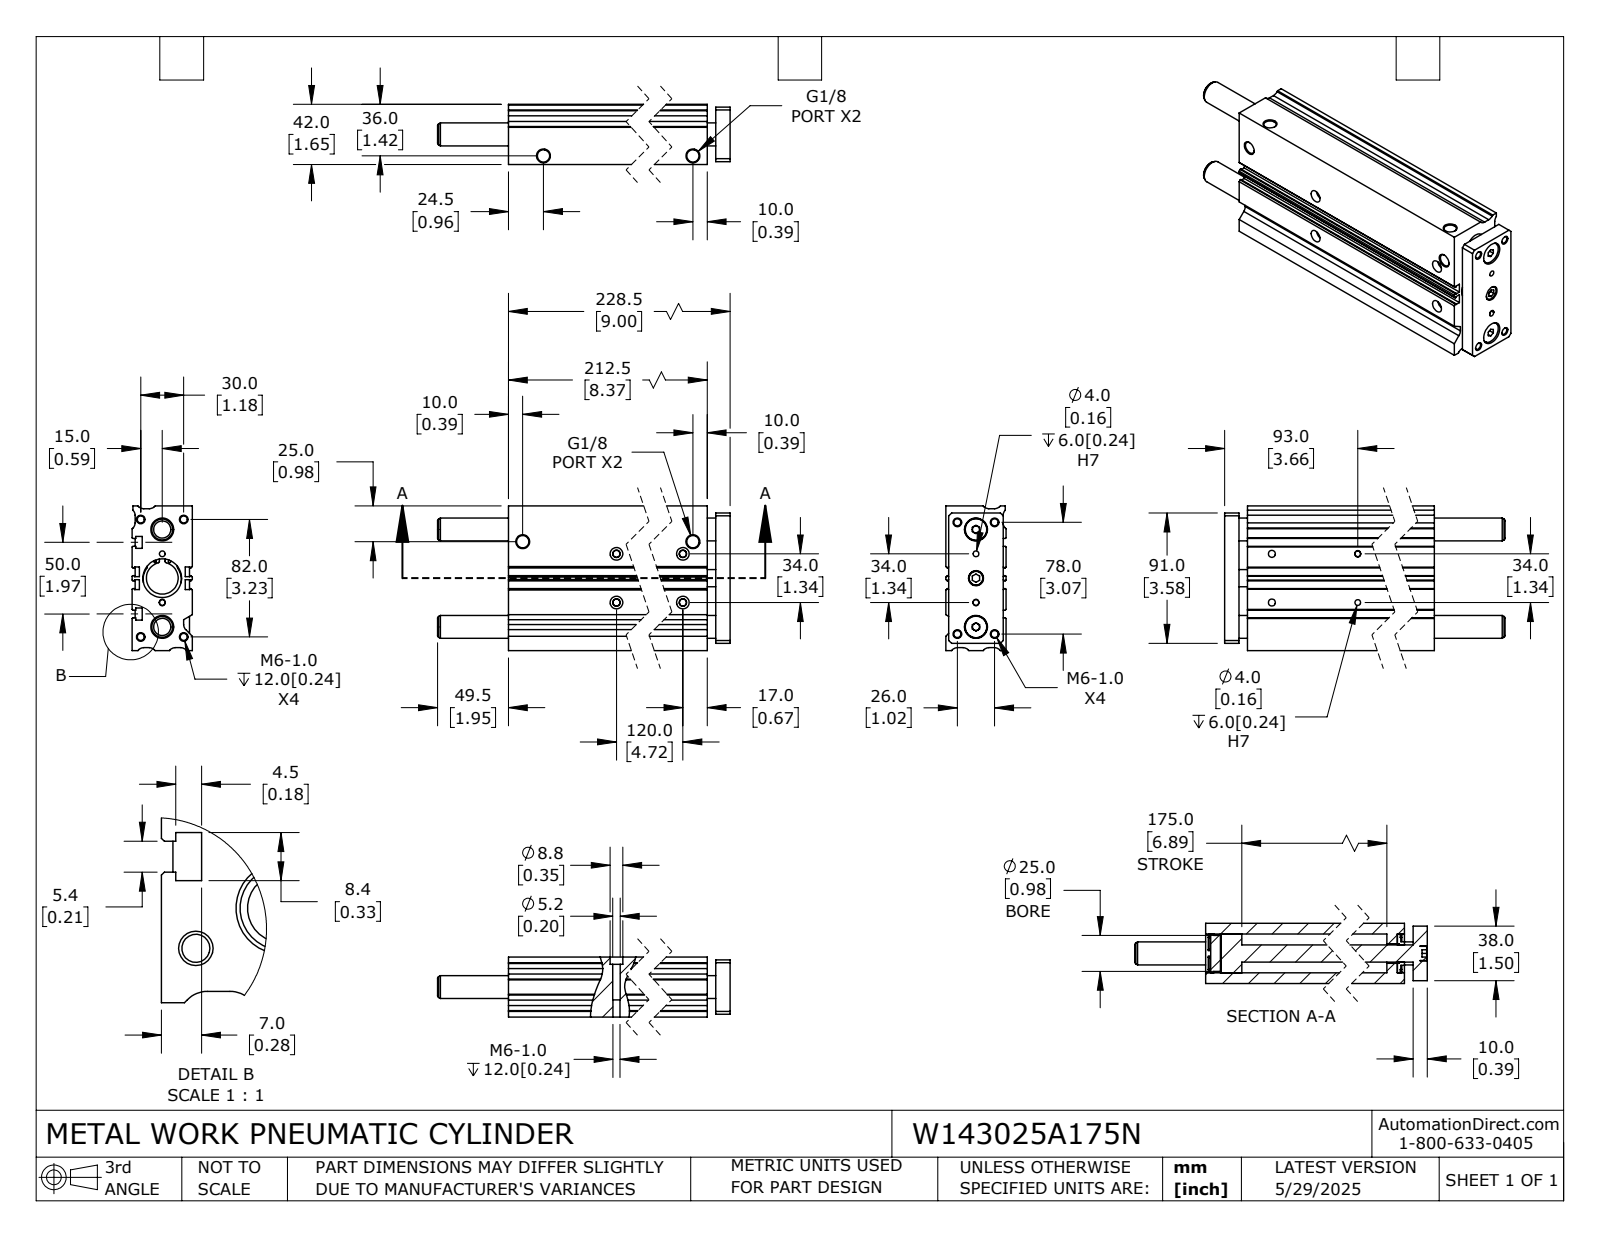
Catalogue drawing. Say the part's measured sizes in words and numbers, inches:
The part is named "W143025A175N_ROD; W143025A175N; W143025A175N_BODY". Its 3-D file was written by "SolidWorks 2024 (CONFIG_CONTROL_DESIGN)". It is 6 solids with 390 faces: 191 planar, 157 cylindrical and 42 other. Overall it measures 10.945 by 3.976 by 1.654 inches. Its volume is 48.04 cubic inches and its surface area 284.7 square inches. Round holes: 8 of diameter 0.194, 4 of diameter 0.067, 4 of diameter 0.157, 4 of diameter 0.194, 4 of diameter 0.205, 4 of diameter 0.337, 4 of diameter 0.346, 2 of diameter 0.63, 1 of diameter 0.413, 1 of diameter 0.472, 1 of diameter 0.539, 1 of diameter 0.874. Round bosses or shafts: 2 of diameter 0.61, 1 of diameter 1.063, 1 of diameter 0.984, 1 of diameter 0.65, 1 of diameter 0.394. Partial cylindrical surfaces (rounded edges, fillets, slot ends): 12 of radius 0.039, 9 of radius 0.197, 8 of radius 0.079, 2 of radius 0.524, 1 of radius 0.559. The main face-to-face distances are 1.654, 0.079, 0.197, 1.378, 1.457, 0.839, 3.976, 2.299, 0.236, 0.276. The hole center spacings are 1.339, 0.111, 0.29, 0.5, 0.548, 0.652, 0.669, 0.902.
